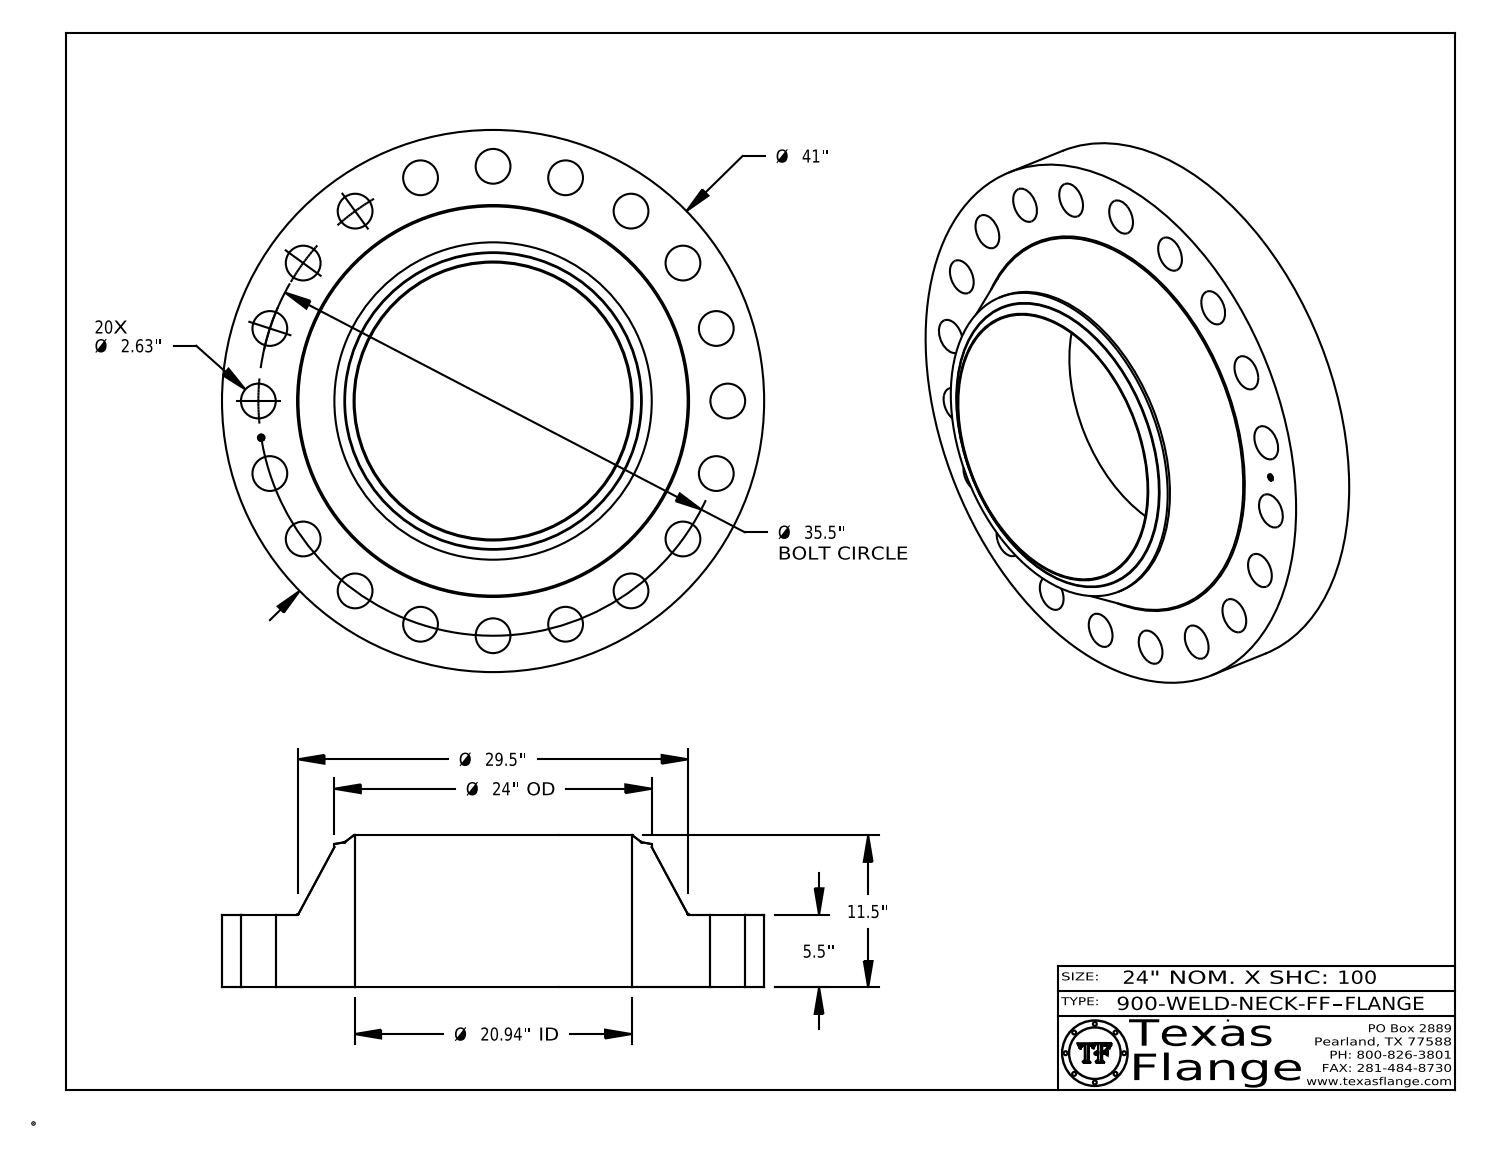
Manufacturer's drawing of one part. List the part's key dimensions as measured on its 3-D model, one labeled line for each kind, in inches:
Part name (STEP PRODUCT): 900-WELD-NECK-FF
STEP written by: CATIA V5 STEP AP214 (AUTOMOTIVE_DESIGN)
Units: inches
Bodies: 1 solid, 444 faces (368 planar, 66 cylindrical, 10 other)
Overall size (bounding box): 41 × 41 × 11.5
Volume: 5 944 in³ · Surface area: 4 394 in²
Round holes (diameter × count): ⌀2.63 ×20, ⌀0.495 ×1, ⌀20.938 ×1
Round bosses / shafts (diameter × count): ⌀0.03 ×8, ⌀41 ×1, ⌀24 ×1, ⌀0.39 ×1
Main face-to-face distances: 5.5, 11.5, 6, 5.485, 0.015, 6.015, 0.148, 0.144, 0.027, 0.096
Hole centre spacings: 17.75, 10.97, 28.72, 31.631, 16.117, 20.866, 25.102, 33.762
